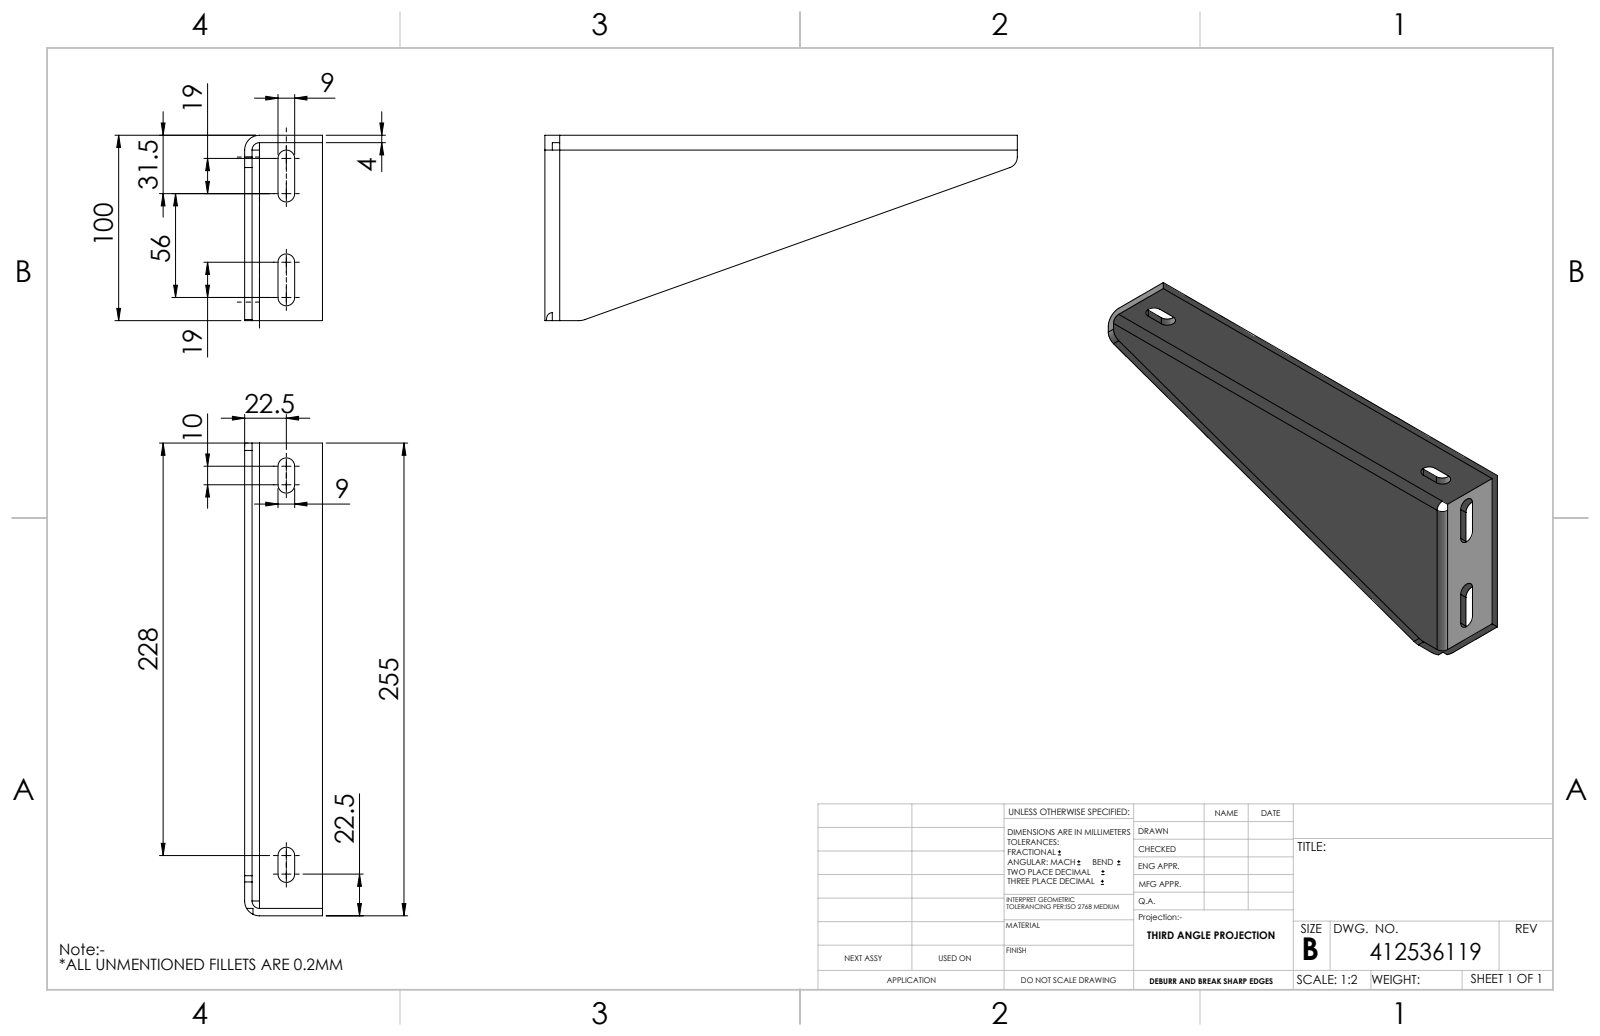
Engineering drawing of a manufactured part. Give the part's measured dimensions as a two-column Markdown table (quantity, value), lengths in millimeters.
| quantity | value |
| --- | --- |
| part name | 412536119 Konsole links l=255 |
| STEP written by | Autodesk Inventor 2016 (AUTOMOTIVE_DESIGN) |
| units | millimeters |
| bodies | 1 solid, 41 faces (26 planar, 15 cylindrical, 0 other) |
| overall size | 255 × 100 × 42 |
| volume | 108 794 mm³ |
| surface area | 58 273 mm² |
| partial cylindrical surfaces (radius × count) | 4.5 × 9, 4 × 2, 8 × 2, 6 × 1, 10 × 1 |
| main face-to-face distances | 4, 42, 38, 18, 27, 14, 23, 9, 24, 15 |
